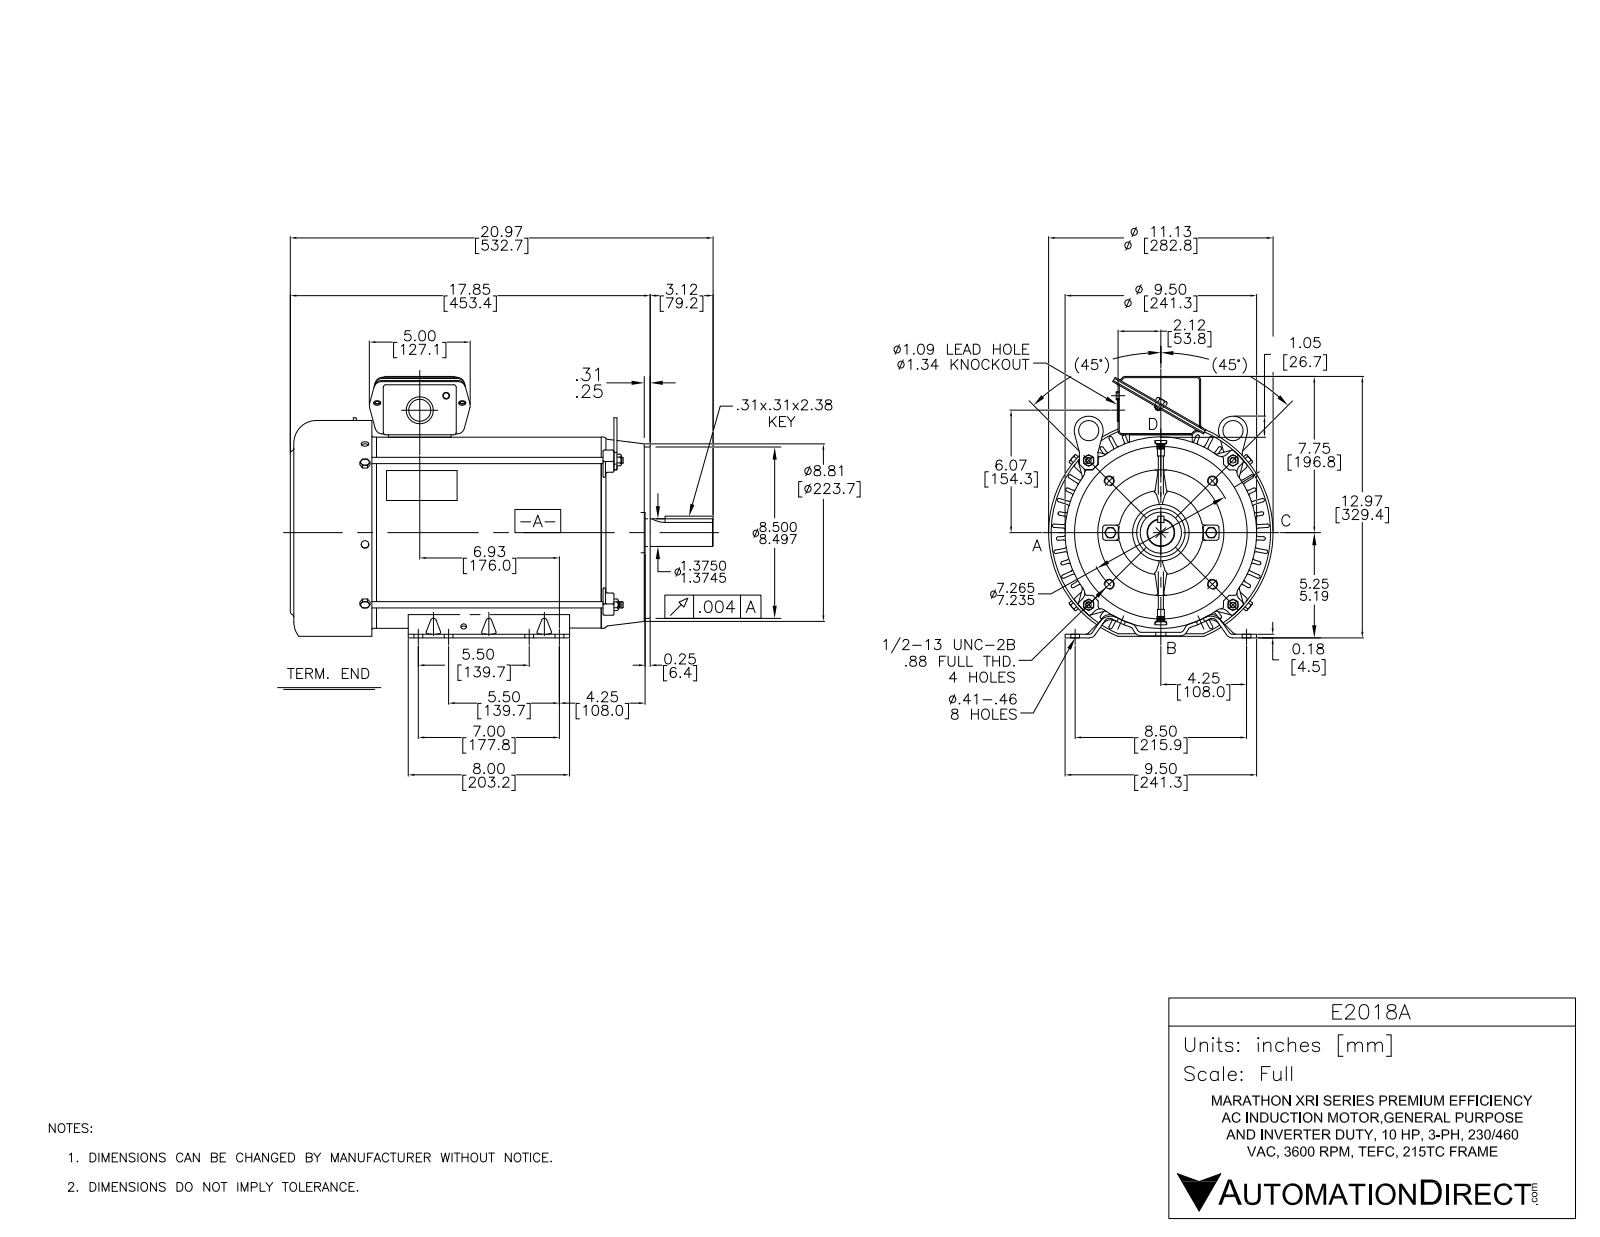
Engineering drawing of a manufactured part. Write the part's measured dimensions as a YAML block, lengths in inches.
part_name: "E2014A r1"
step_written_by: "SolidWorks 2017 (AUTOMOTIVE_DESIGN)"
units: inches
bodies: {solids: 30, faces: 3327, planar: 1052, cylindrical: 1045, other: 1230}
overall_size: [20.966, 12.914, 11.16]
volume: 181.9
surface_area: 2099
round_holes:
  - {diameter: 0.373, count: 10}
  - {diameter: 0.435, count: 8}
  - {diameter: 0.257, count: 4}
  - {diameter: 0.32, count: 4}
  - {diameter: 0.37, count: 4}
  - {diameter: 0.422, count: 4}
  - {diameter: 0.219, count: 3}
  - {diameter: 0.267, count: 3}
  - {diameter: 0.176, count: 2}
  - {diameter: 0.218, count: 2}
  - {diameter: 0.279, count: 2}
  - {diameter: 0.34, count: 2}
round_bosses_or_shafts:
  - {diameter: 0.31, count: 10}
  - {diameter: 0.44, count: 6}
  - {diameter: 0.399, count: 2}
  - {diameter: 0.295, count: 2}
  - {diameter: 0.19, count: 2}
  - {diameter: 9.489, count: 1}
  - {diameter: 9.271, count: 1}
  - {diameter: 8.499, count: 1}
partial_cylinders:
  - {radius: 0.13, count: 149}
  - {radius: 0.06, count: 134}
  - {radius: 0.12, count: 86}
  - {radius: 0.25, count: 34}
  - {radius: 0.03, count: 12}
  - {radius: 0.18, count: 10}
  - {radius: 0.04, count: 8}
  - {radius: 0.14, count: 8}
face_to_face_distances: [0.06, 0.17, 17.675, 0.12, 0.179, 0.1, 2.734, 17.845, 0.179, 0.11]
hole_center_spacings: [6.224, 2.5, 7.156, 1, 1.435, 1.5, 2.564, 3.5]
